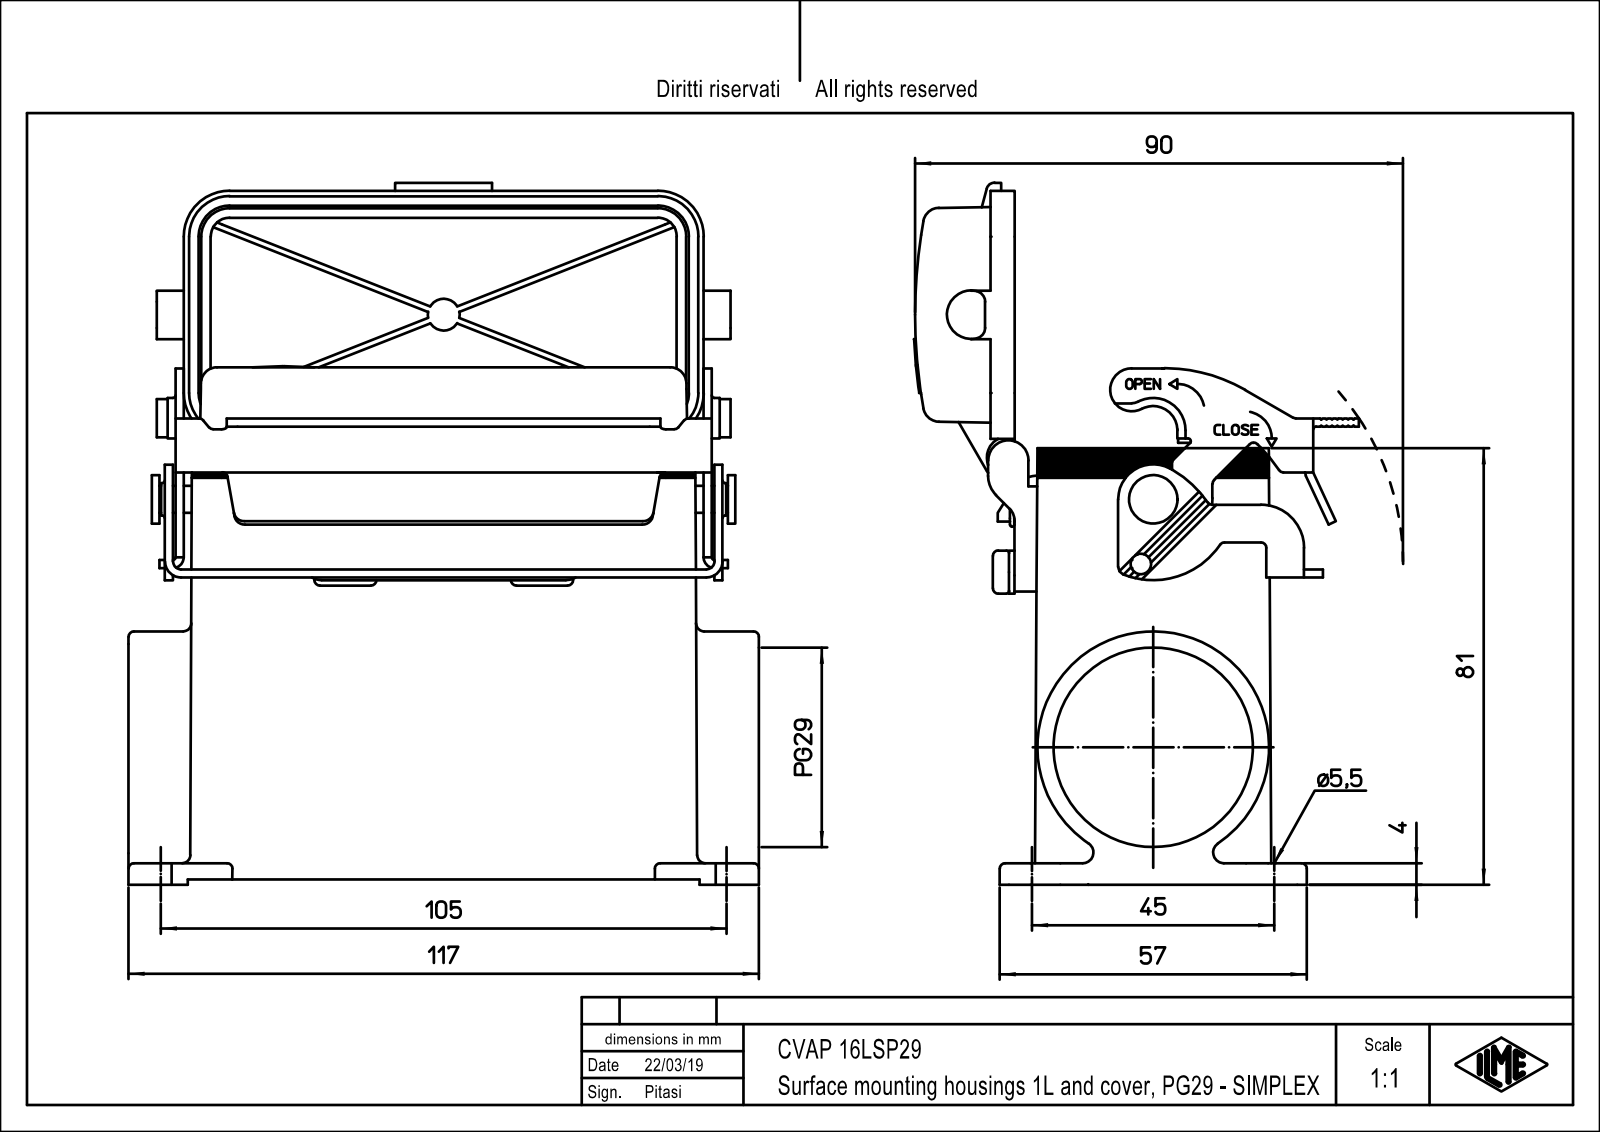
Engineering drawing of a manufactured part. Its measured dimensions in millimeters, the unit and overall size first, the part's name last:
Units: millimetres
Overall size (bounding box): 126.72 × 117 × 79.7
Round holes (diameter × count): ⌀2.46 ×4, ⌀3 ×4, ⌀5.5 ×4, ⌀32 ×1, ⌀37 ×1
Round bosses / shafts (diameter × count): ⌀0.8 ×3, ⌀44.5 ×1, ⌀9 ×1, ⌀8.4 ×1, ⌀8 ×1, ⌀6 ×1, ⌀5 ×1, ⌀2.4 ×1
Partial cylindrical surfaces — rounded edges, fillets, slot ends (radius × count): R2 ×22, R3 ×13, R1.5 ×8, R3.5 ×7, R1 ×5, R6 ×5, R0.5 ×4, R1.8 ×4
Main face-to-face distances: 4, 40.5, 44.5, 36.5, 1.5, 2, 7.5, 3.5, 11.5, 82
Hole centre spacings: 16.43, 38.54, 91.69, 98.09, 27, 45, 77.5, 82.07
Volume: 146 405 mm³ · Surface area: 86 684 mm²
Bodies: 1 solid, 621 faces (384 planar, 213 cylindrical, 24 other)
Part name (STEP PRODUCT): CVAP_16LSP29
STEP written by: PTC Creo Elements/Direct Modeling 19.0E 27-Jun-2016 (C) Parametric Technology GmbH (AUTOMOTIVE_DESIGN)
